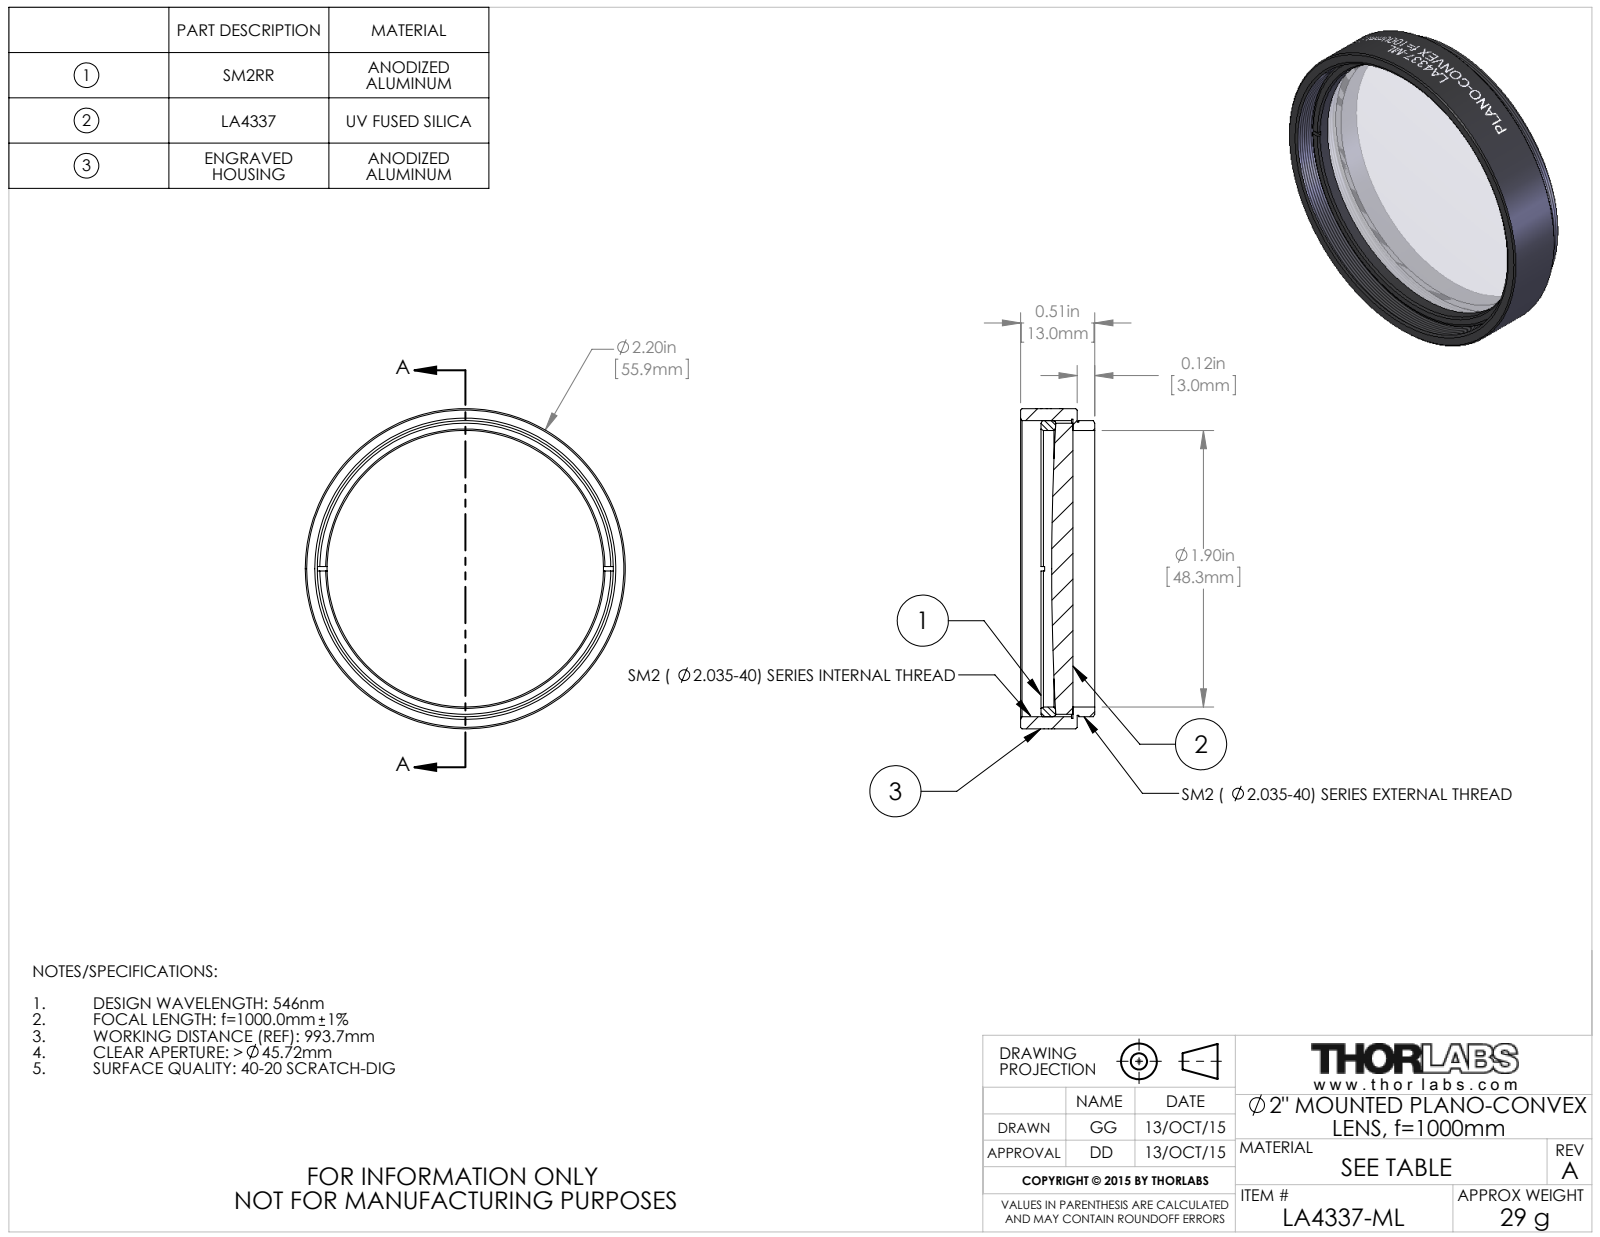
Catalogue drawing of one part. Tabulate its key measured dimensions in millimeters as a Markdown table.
| quantity | value |
| --- | --- |
| part name | TTN039248-E0W |
| STEP written by | SolidWorks 2014 (CONFIG_CONTROL_DESIGN) |
| units | millimeters |
| bodies | 3 solids, 110 faces (16 planar, 74 cylindrical, 20 other) |
| overall size | 55.88 × 55.88 × 12.95 |
| volume | 11 919 mm³ |
| surface area | 11 351 mm² |
| round holes (diameter × count) | 48.26 × 1, 52.2 × 1 |
| round bosses / shafts (diameter × count) | 55.88 × 1, 51.69 × 1, 51.18 × 1, 50.8 × 1 |
| main face-to-face distances | 3.05, 3.81, 0.76, 9.91, 9.15, 12.96, 6.86, 6.1, 9.4, 6.35 |
